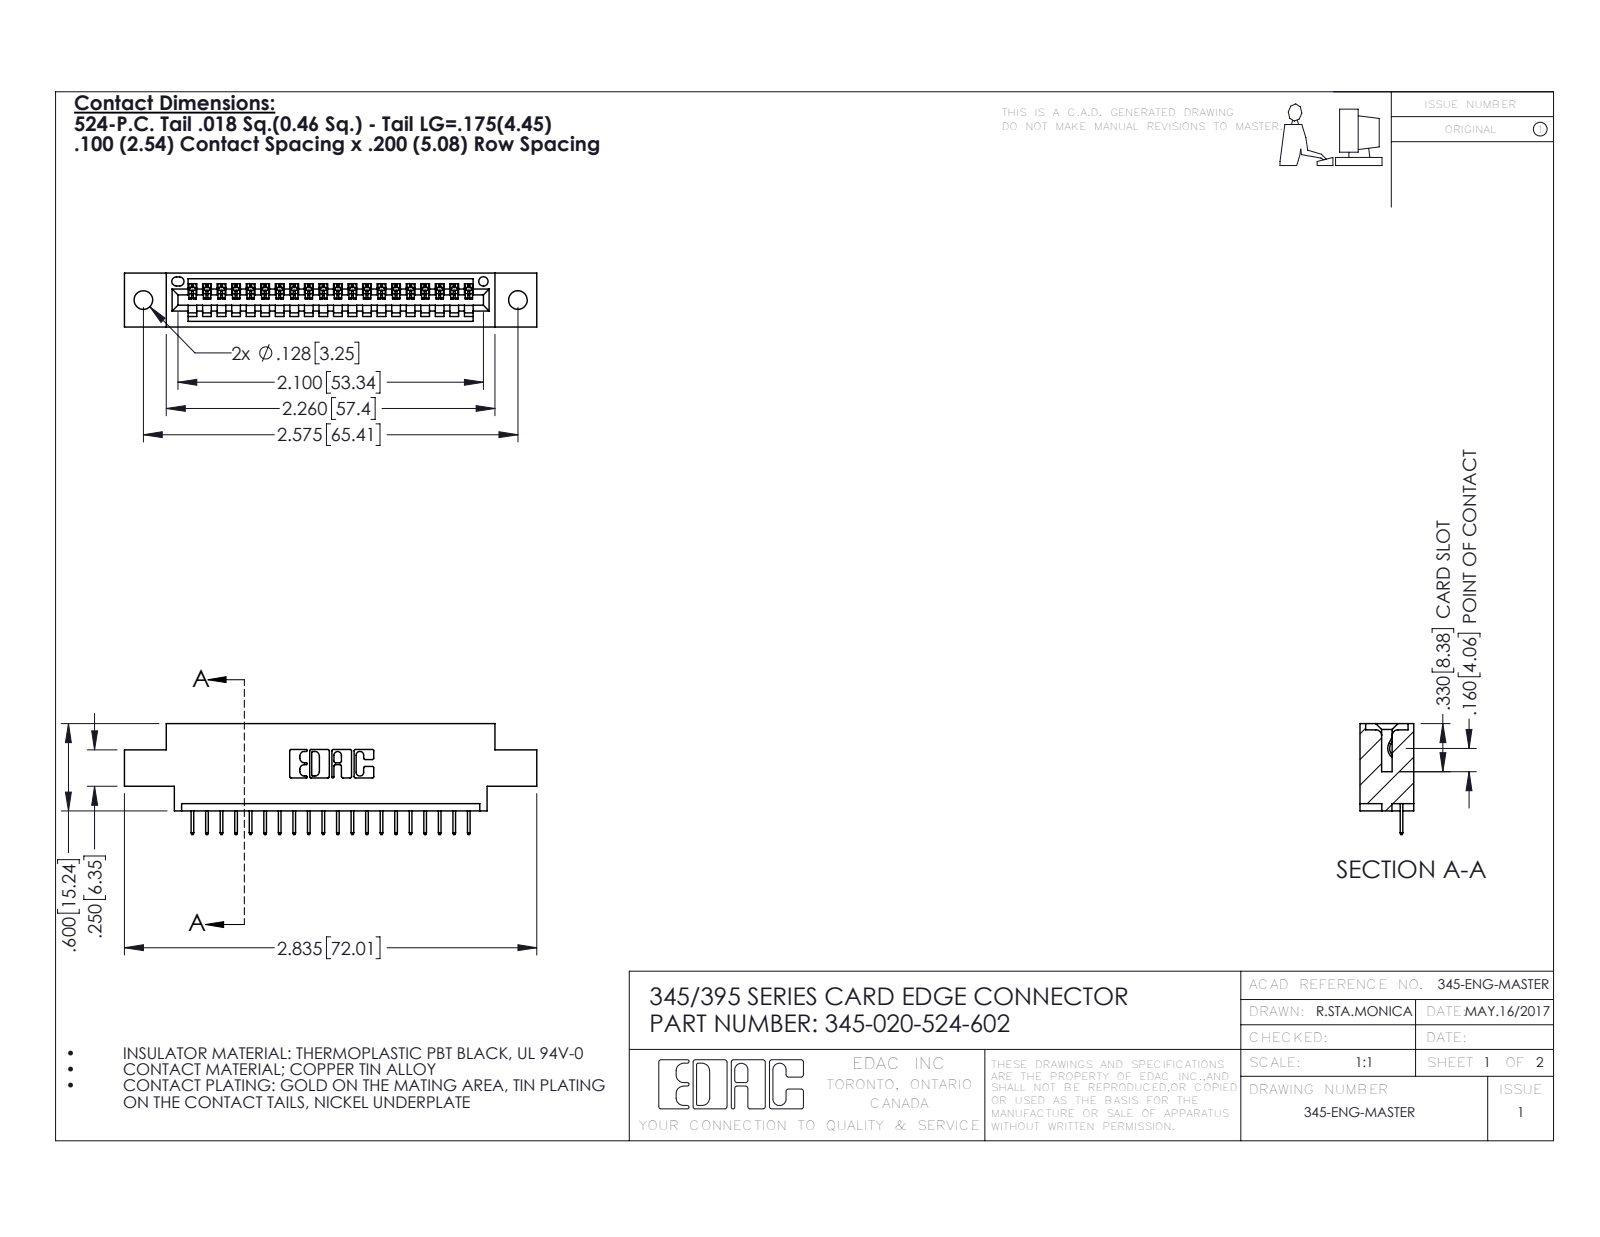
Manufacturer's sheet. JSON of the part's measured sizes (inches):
{"part_name": "345-292-001_345-293-124; 345 Part_0.170 Offset - 0.128 Dia; 345-020-524-602", "step_written_by": "SolidWorks 2016 (CONFIG_CONTROL_DESIGN)", "units": "inches", "bodies": {"solids": 21, "faces": 1370, "planar": 1004, "cylindrical": 366, "other": 0}, "overall_size": [2.835, 0.762, 0.37], "volume_in3": 0.392, "surface_area_in2": 12.17, "round_holes": [[0.128, 2], [0.064, 1]], "partial_cylinders_radius": [[0.006, 40], [0.01, 22], [0.007, 6], [0.031, 6], [0.026, 3], [0.031, 2], [0.04, 2], [0.014, 1]], "face_to_face_distances": [0.37, 0.072, 0.298, 0.2, 0.098, 0.272, 0.025, 0.225, 0.072, 0.175], "hole_center_spacings": [0.27, 2.341, 2.575]}
